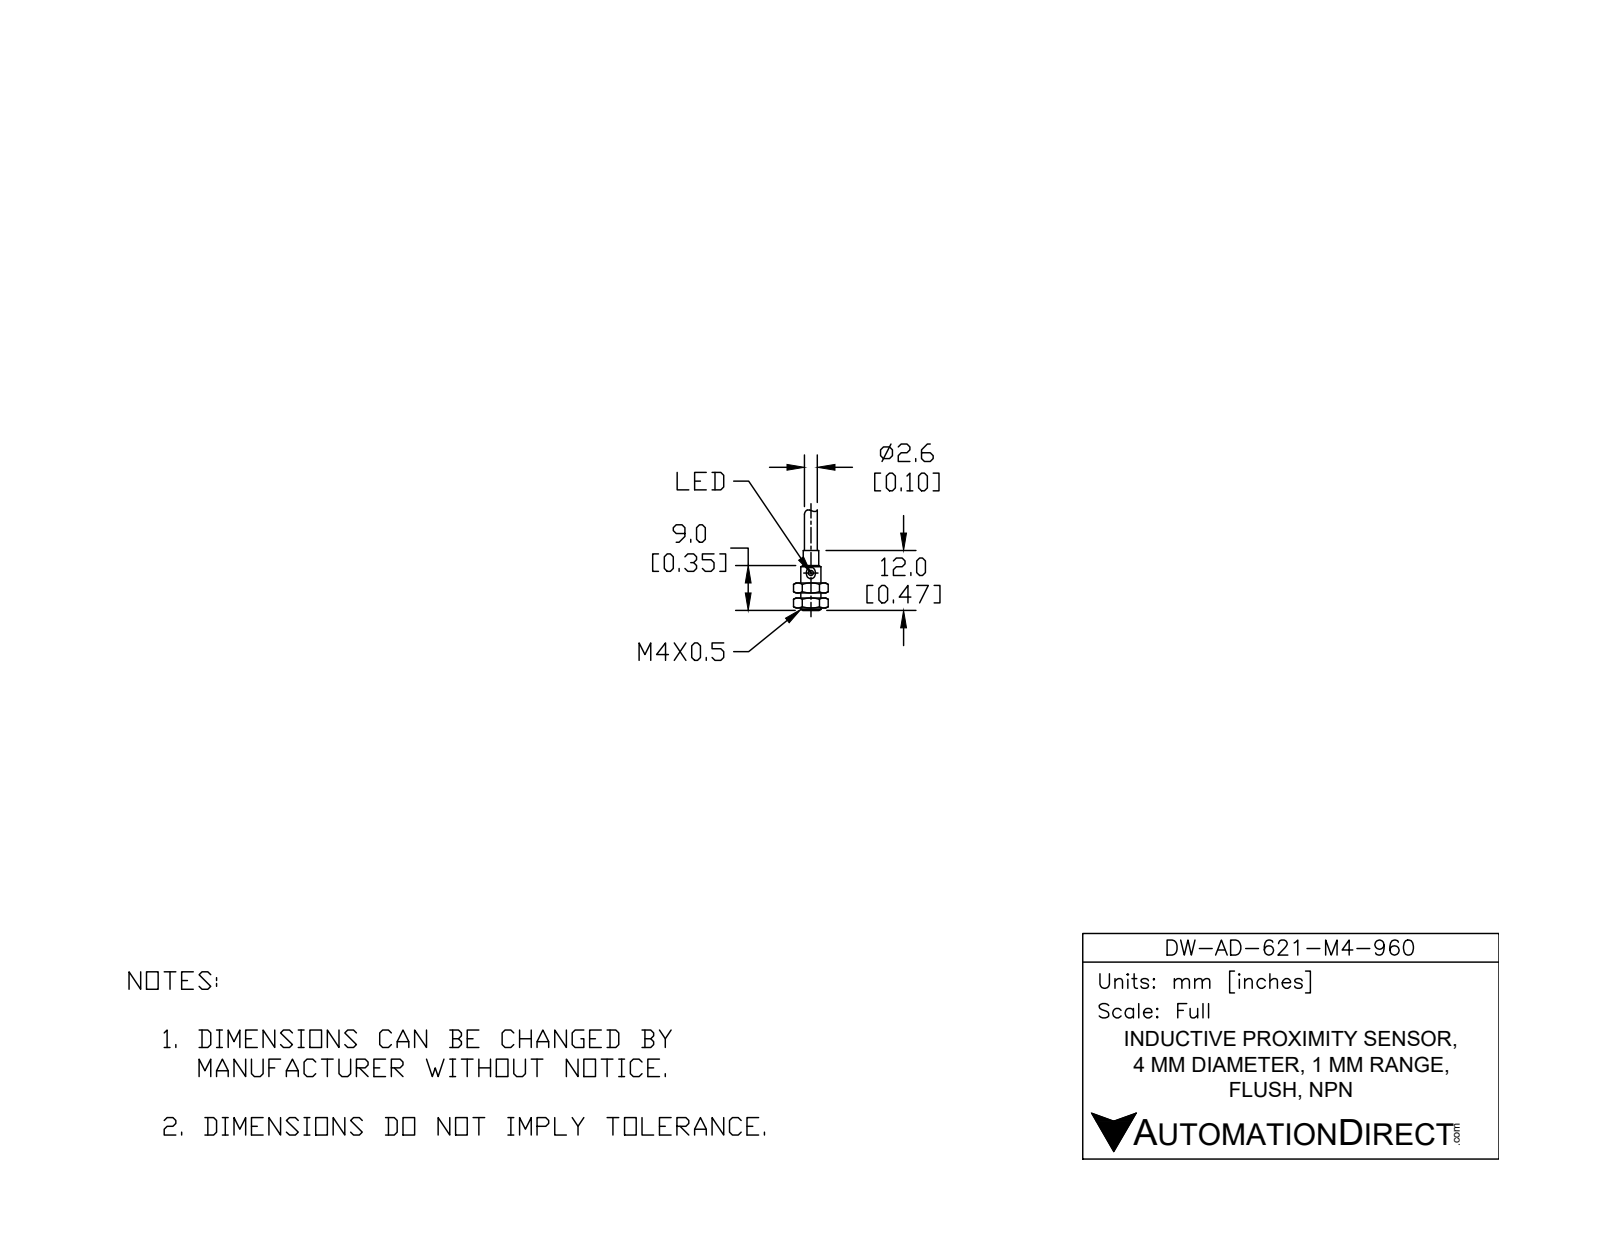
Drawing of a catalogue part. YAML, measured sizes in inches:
part_name: "DW-AD-621-M4-960"
step_written_by: "SolidWorks 2017 (AUTOMOTIVE_DESIGN)"
units: inches
bodies: {solids: 2, faces: 14, planar: 6, cylindrical: 3, other: 5}
overall_size: [0.753, 0.157, 0.157]
volume: 0.014
surface_area: 0.509
round_bosses_or_shafts:
  - {diameter: 0.157, count: 1}
  - {diameter: 0.122, count: 1}
  - {diameter: 0.102, count: 1}
face_to_face_distances: [0.472, 0.469]
